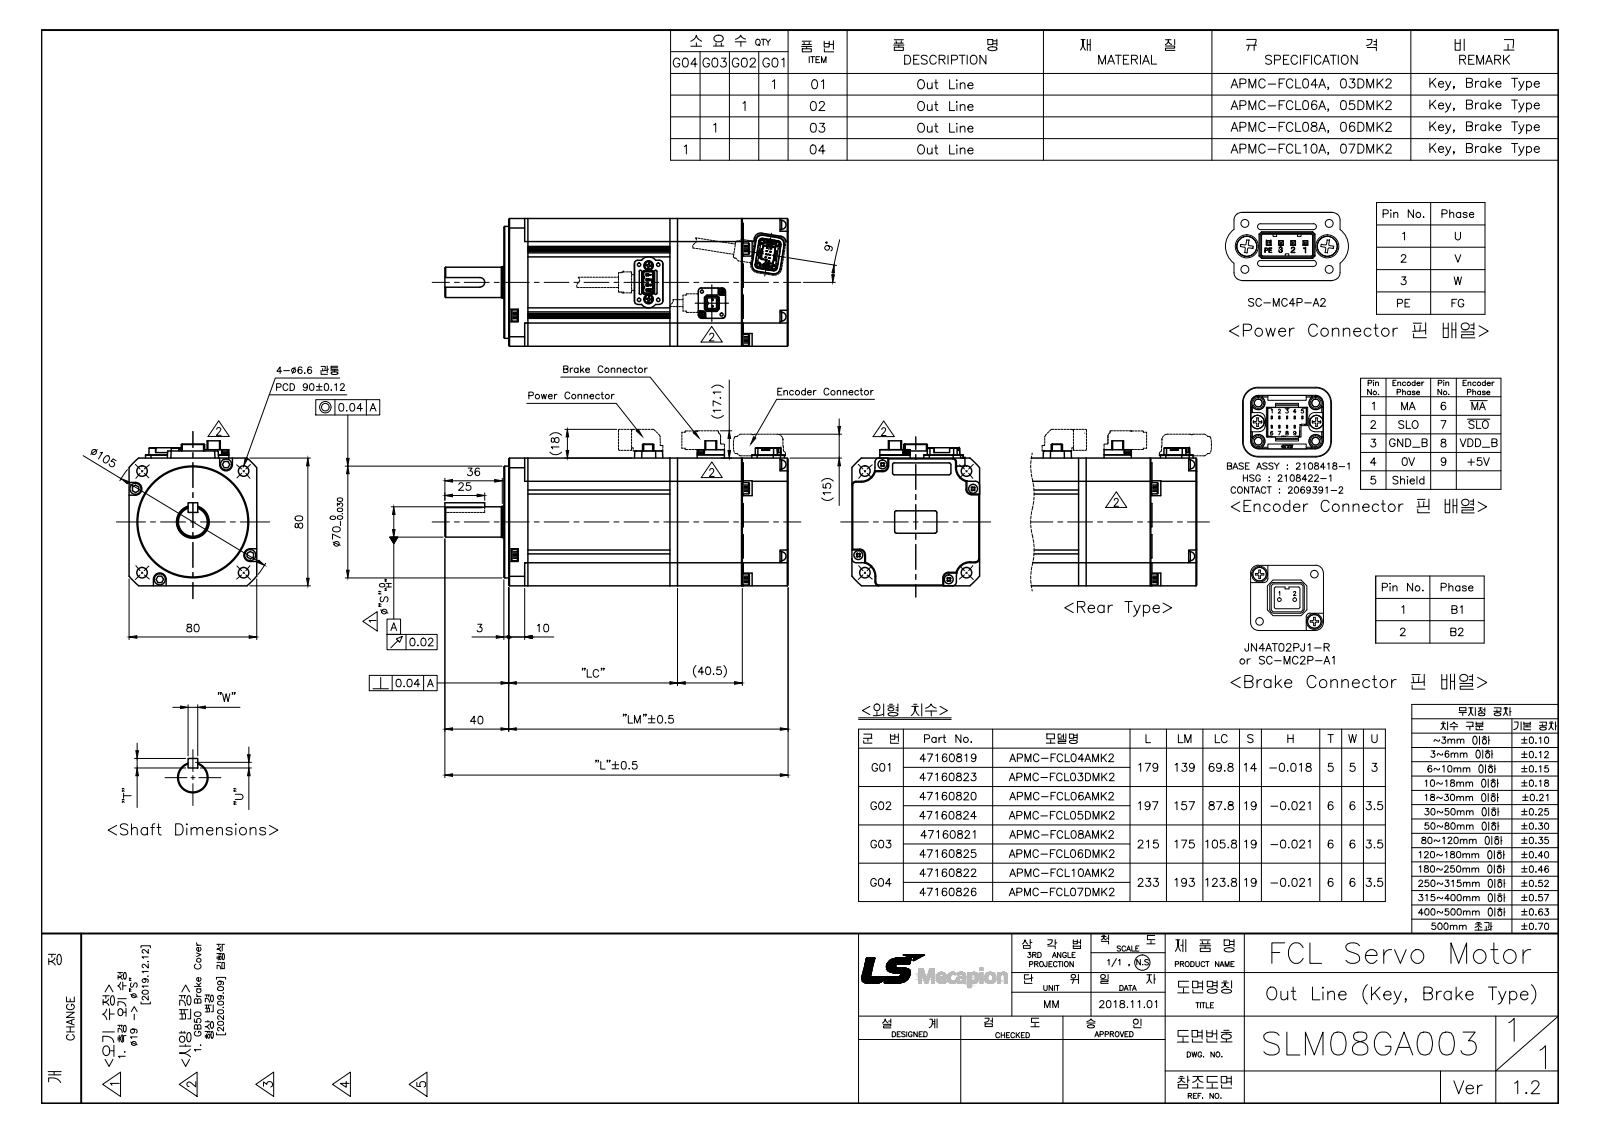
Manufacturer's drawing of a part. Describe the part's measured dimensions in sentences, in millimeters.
The part is named "APMC-FCL08AMK2, FCL06DMK2(Ver.1.1)". Its 3-D file was written by "SolidWorks 2020 (AUTOMOTIVE_DESIGN)". It is 50 solids with 2069 faces: 1307 planar, 549 cylindrical and 213 other. Overall it measures 215 by 90.8 by 80 millimeters. Its volume is 1 005 000 cubic millimeters and its surface area 149 503 square millimeters. Round holes: 10 of diameter 2.1, 8 of diameter 4, 8 of diameter 4.5, 6 of diameter 2, 6 of diameter 3, 4 of diameter 3.5, 4 of diameter 6.6, 2 of diameter 1, 2 of diameter 6, 1 of diameter 3.3, 1 of diameter 3.4, 1 of diameter 13. Round bosses or shafts: 8 of diameter 7.2, 8 of diameter 7, 6 of diameter 5.4, 2 of diameter 4.2, 2 of diameter 3.6, 2 of diameter 3.5, 2 of diameter 2.2, 2 of diameter 0.9. Partial cylindrical surfaces (rounded edges, fillets, slot ends): 36 of radius 0.3, 20 of radius 0.2, 12 of radius 2, 10 of radius 1, 9 of radius 0.15, 9 of radius 2.5, 7 of radius 0.45, 7 of radius 4. The main face-to-face distances are 80, 93.8, 4.8, 89, 46, 40.5, 45.3, 134.3, 0.7, 41.2. The hole center spacings are 41.5, 11.81, 52.73, 58.69, 68.66, 85.76, 6.02, 9.43.
